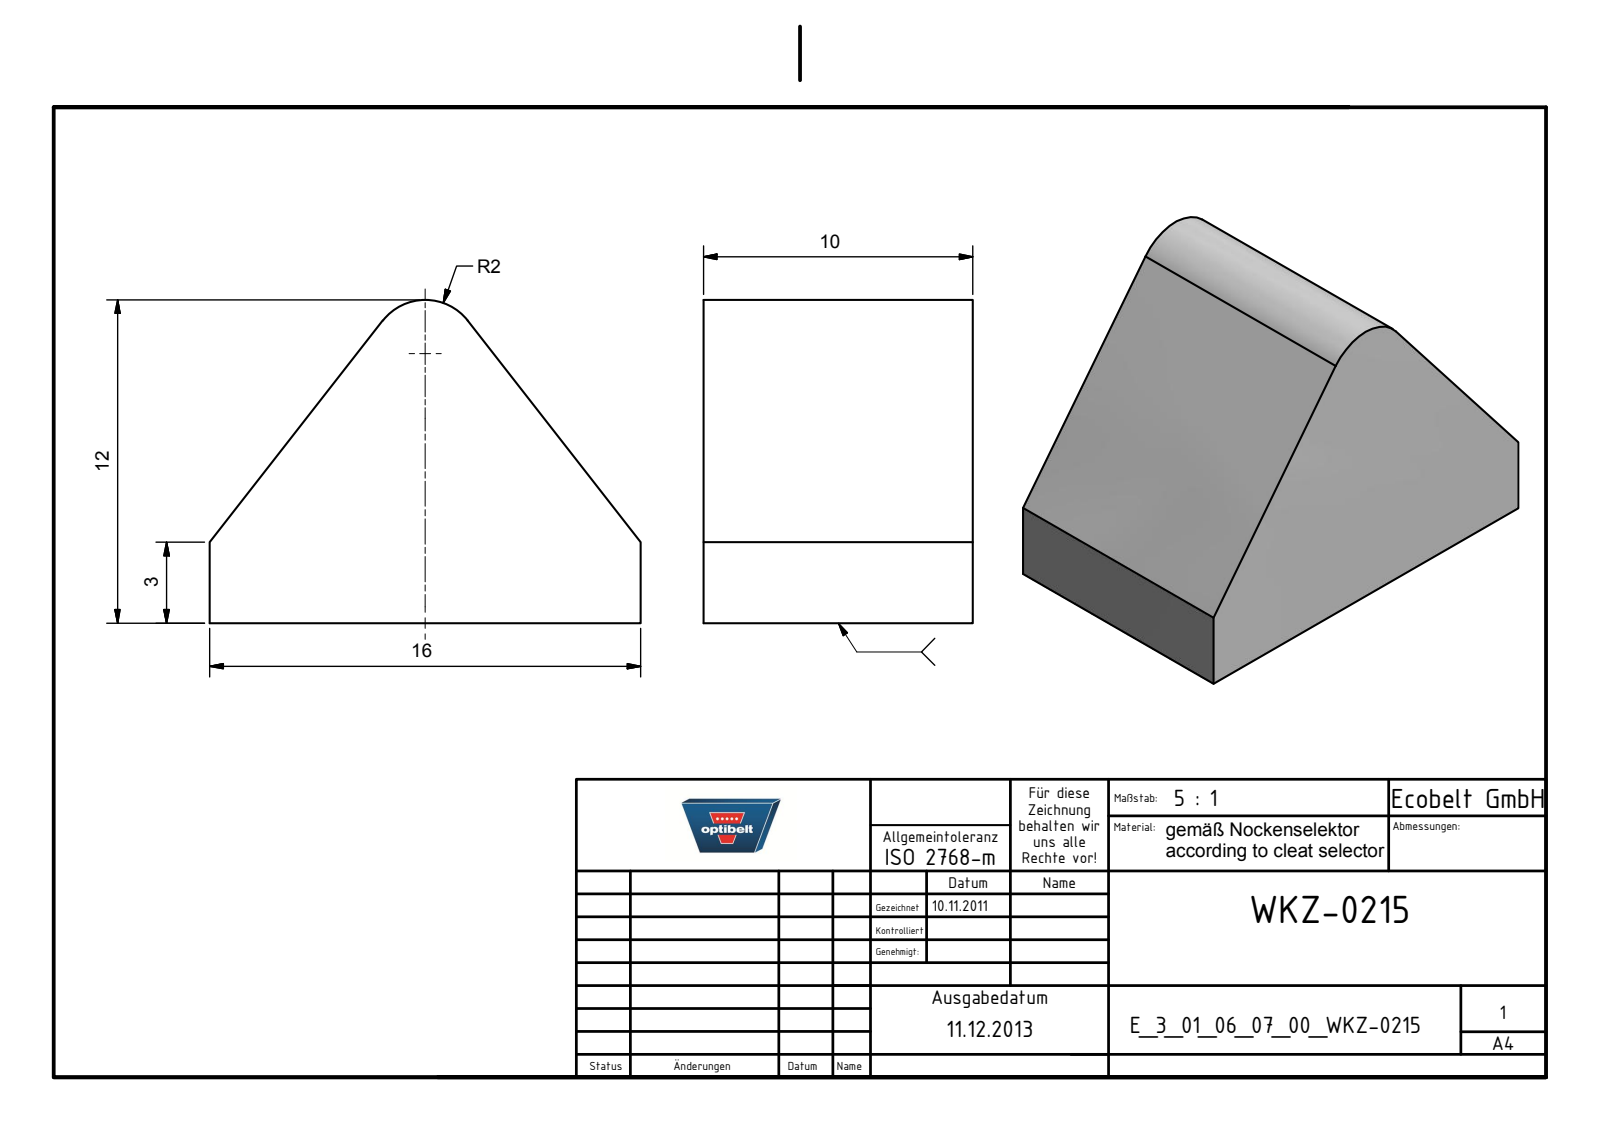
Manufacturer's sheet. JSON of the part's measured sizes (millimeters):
{"part_name": "E_3_01_06_07_00_WKZ-0215", "step_written_by": "Autodesk Inventor 2025 (AUTOMOTIVE_DESIGN)", "units": "millimeters", "bodies": {"solids": 1, "faces": 8, "planar": 7, "cylindrical": 1, "other": 0}, "overall_size": [16, 12, 10], "volume_mm3": 1285, "surface_area_mm2": 722, "partial_cylinders_radius": [[2, 1]], "face_to_face_distances": [10, 16]}
